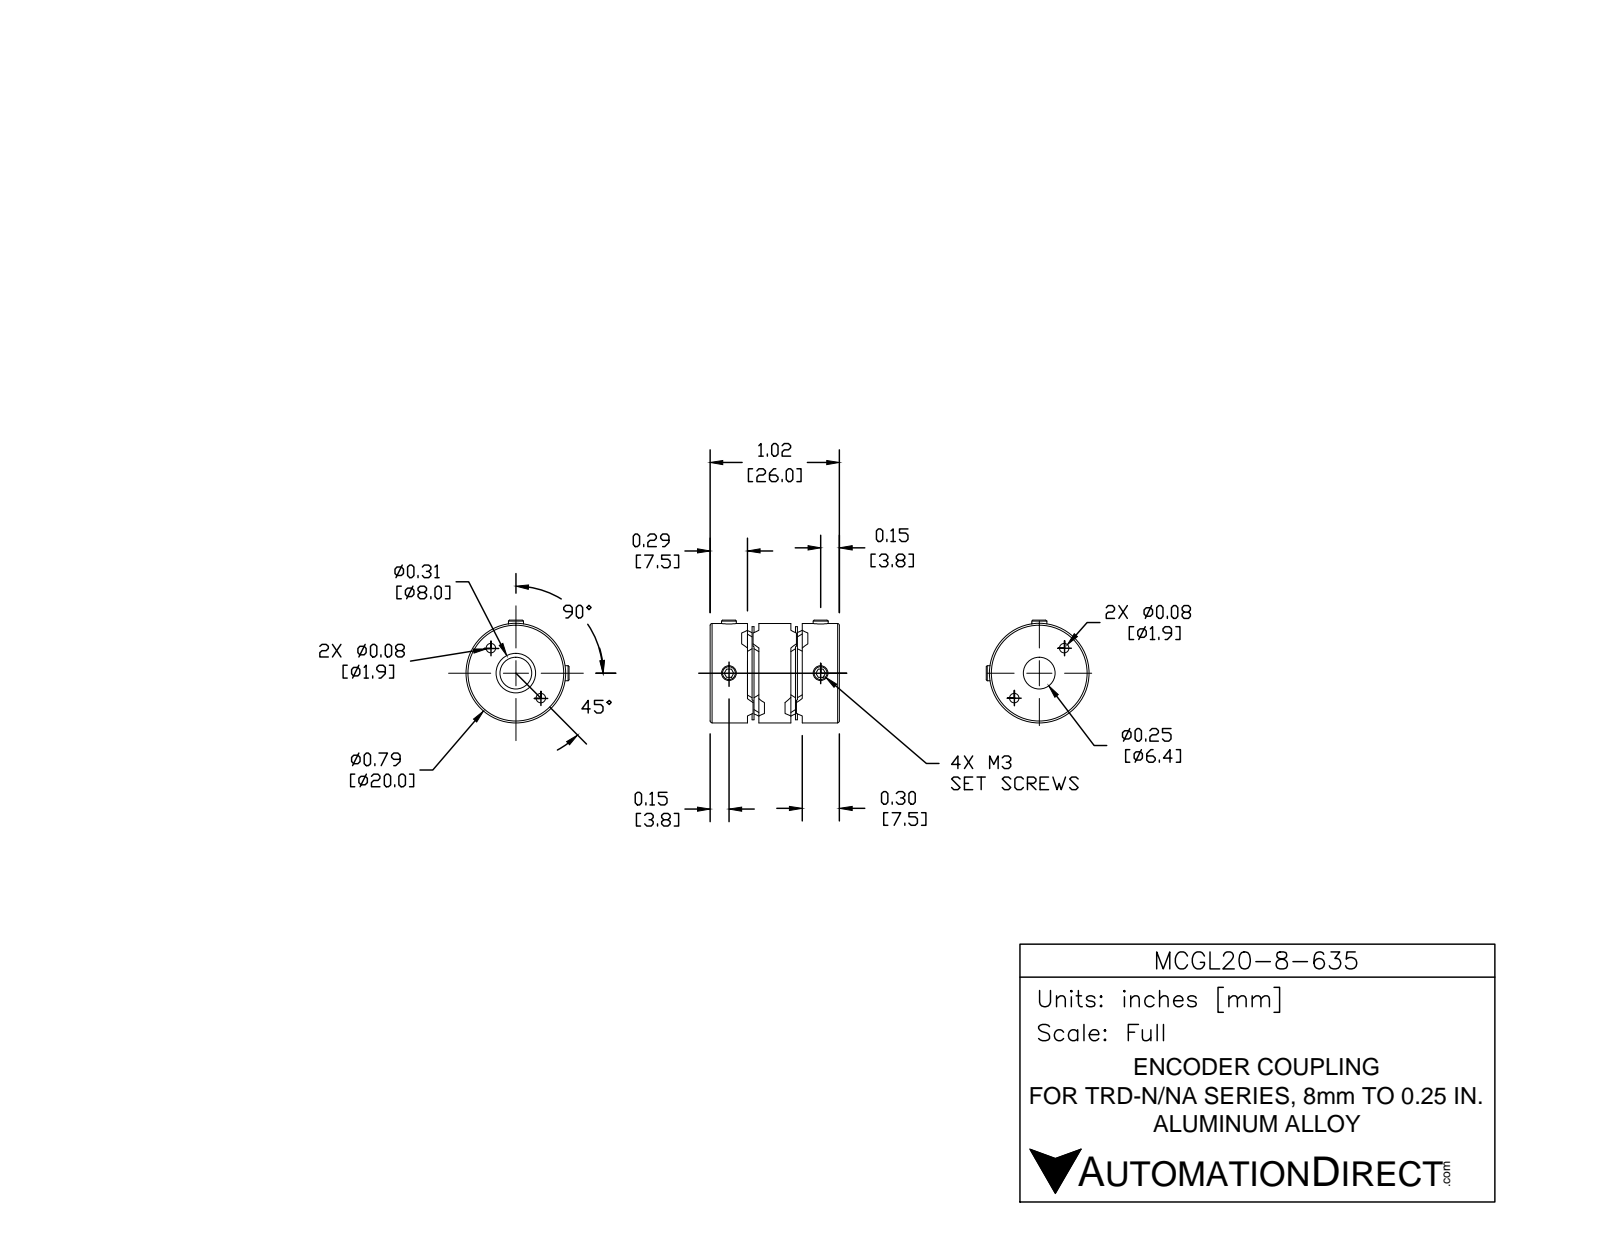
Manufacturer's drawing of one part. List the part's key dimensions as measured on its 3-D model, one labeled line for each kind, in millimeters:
Part name (STEP PRODUCT): MCGL20-8-635
STEP written by: SolidWorks 2016 (AUTOMOTIVE_DESIGN)
Units: millimetres
Bodies: 1 solid, 158 faces (86 planar, 36 cylindrical, 36 other)
Overall size (bounding box): 26 × 20 × 20
Volume: 5 409 mm³ · Surface area: 4 652 mm²
Round holes (diameter × count): ⌀3 ×6, ⌀6.35 ×1, ⌀8 ×1, ⌀9 ×1
Round bosses / shafts (diameter × count): ⌀20 ×1
Main face-to-face distances: 1.4, 7.4, 2.2, 17.1, 8.9, 7.5, 9.6, 0.8, 9.7, 16.3
Hole centre spacings: 7.3, 18.6, 14.6
